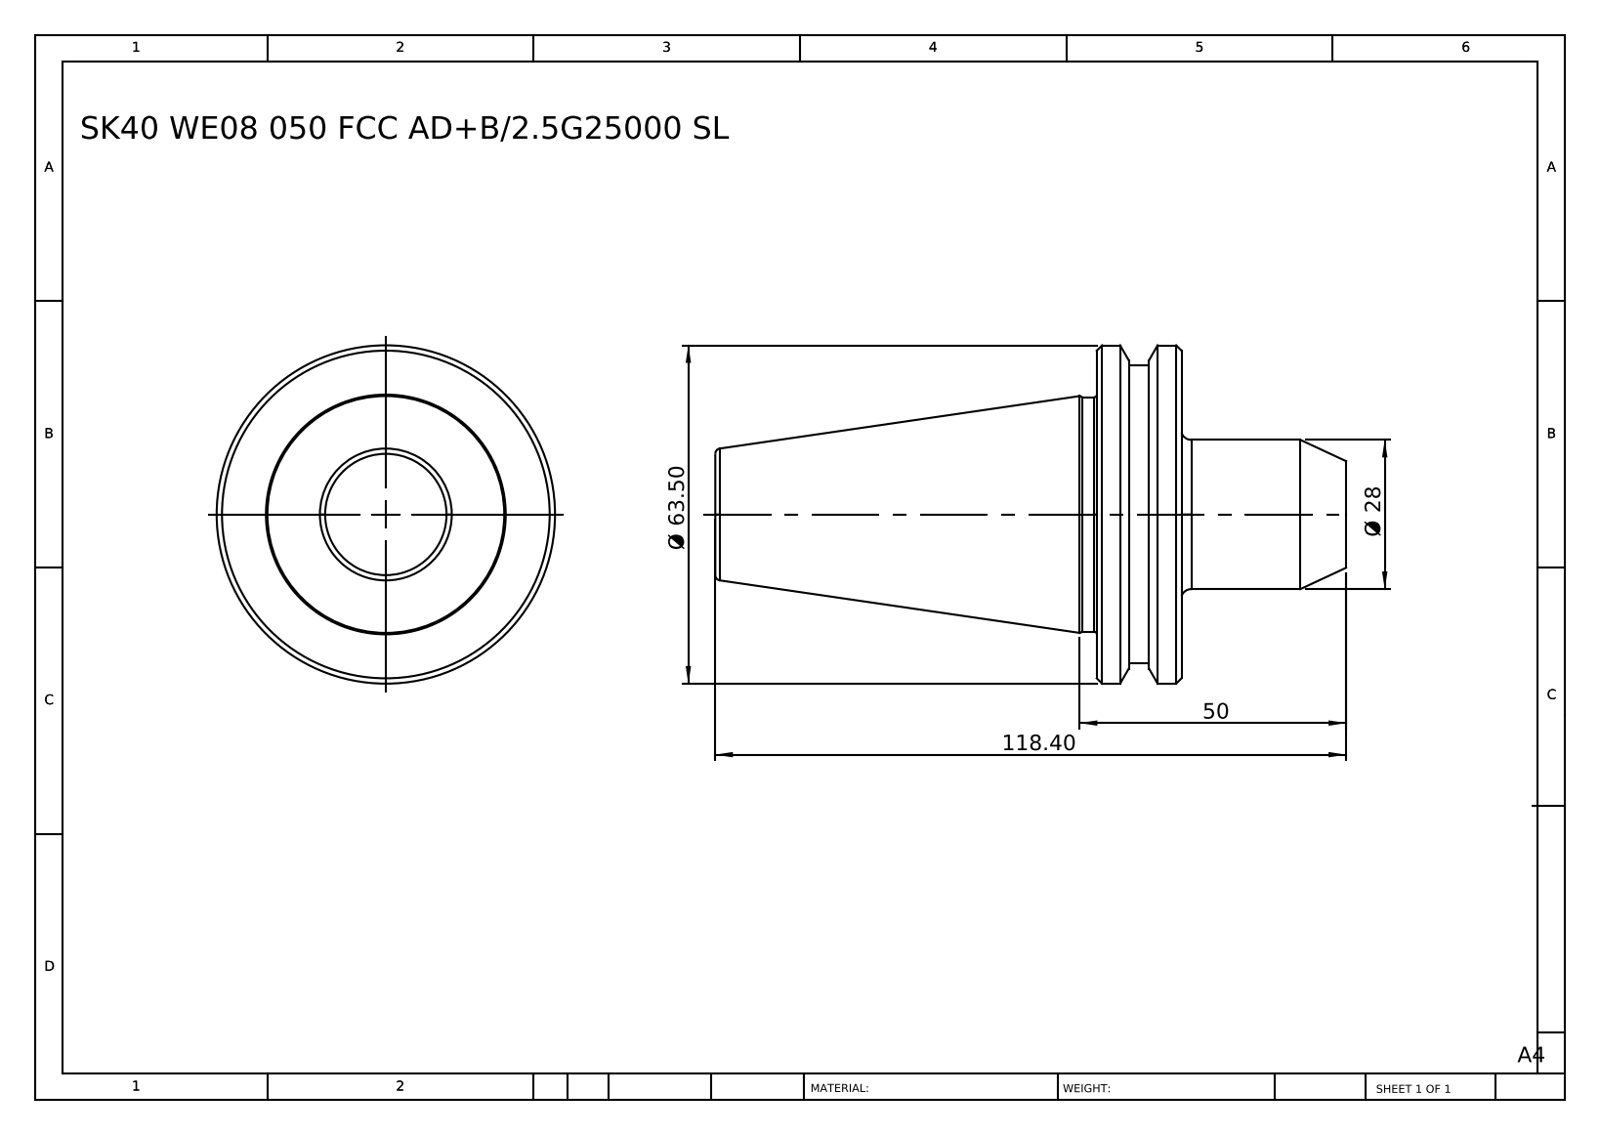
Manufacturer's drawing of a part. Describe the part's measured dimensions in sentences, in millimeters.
The part is named "SK40 WE08 050 AD-6.3G15000 SL". Its 3-D file was written by "SolidWorks 2014 (CONFIG_CONTROL_DESIGN)". It is 1 solid with 36 faces: 6 planar, 10 cylindrical and 20 other. Overall it measures 118.4 by 63.5 by 63.5 millimeters. Its volume is 134 823 cubic millimeters and its surface area 19 250 square millimeters. Round bosses or shafts: 1 of diameter 63.5, 1 of diameter 56, 1 of diameter 44, 1 of diameter 28. The main face-to-face distances are 15.9, 87.5, 71.6, 30.9, 46.8, 118.4, 40.8, 9.9, 6, 77.6.
